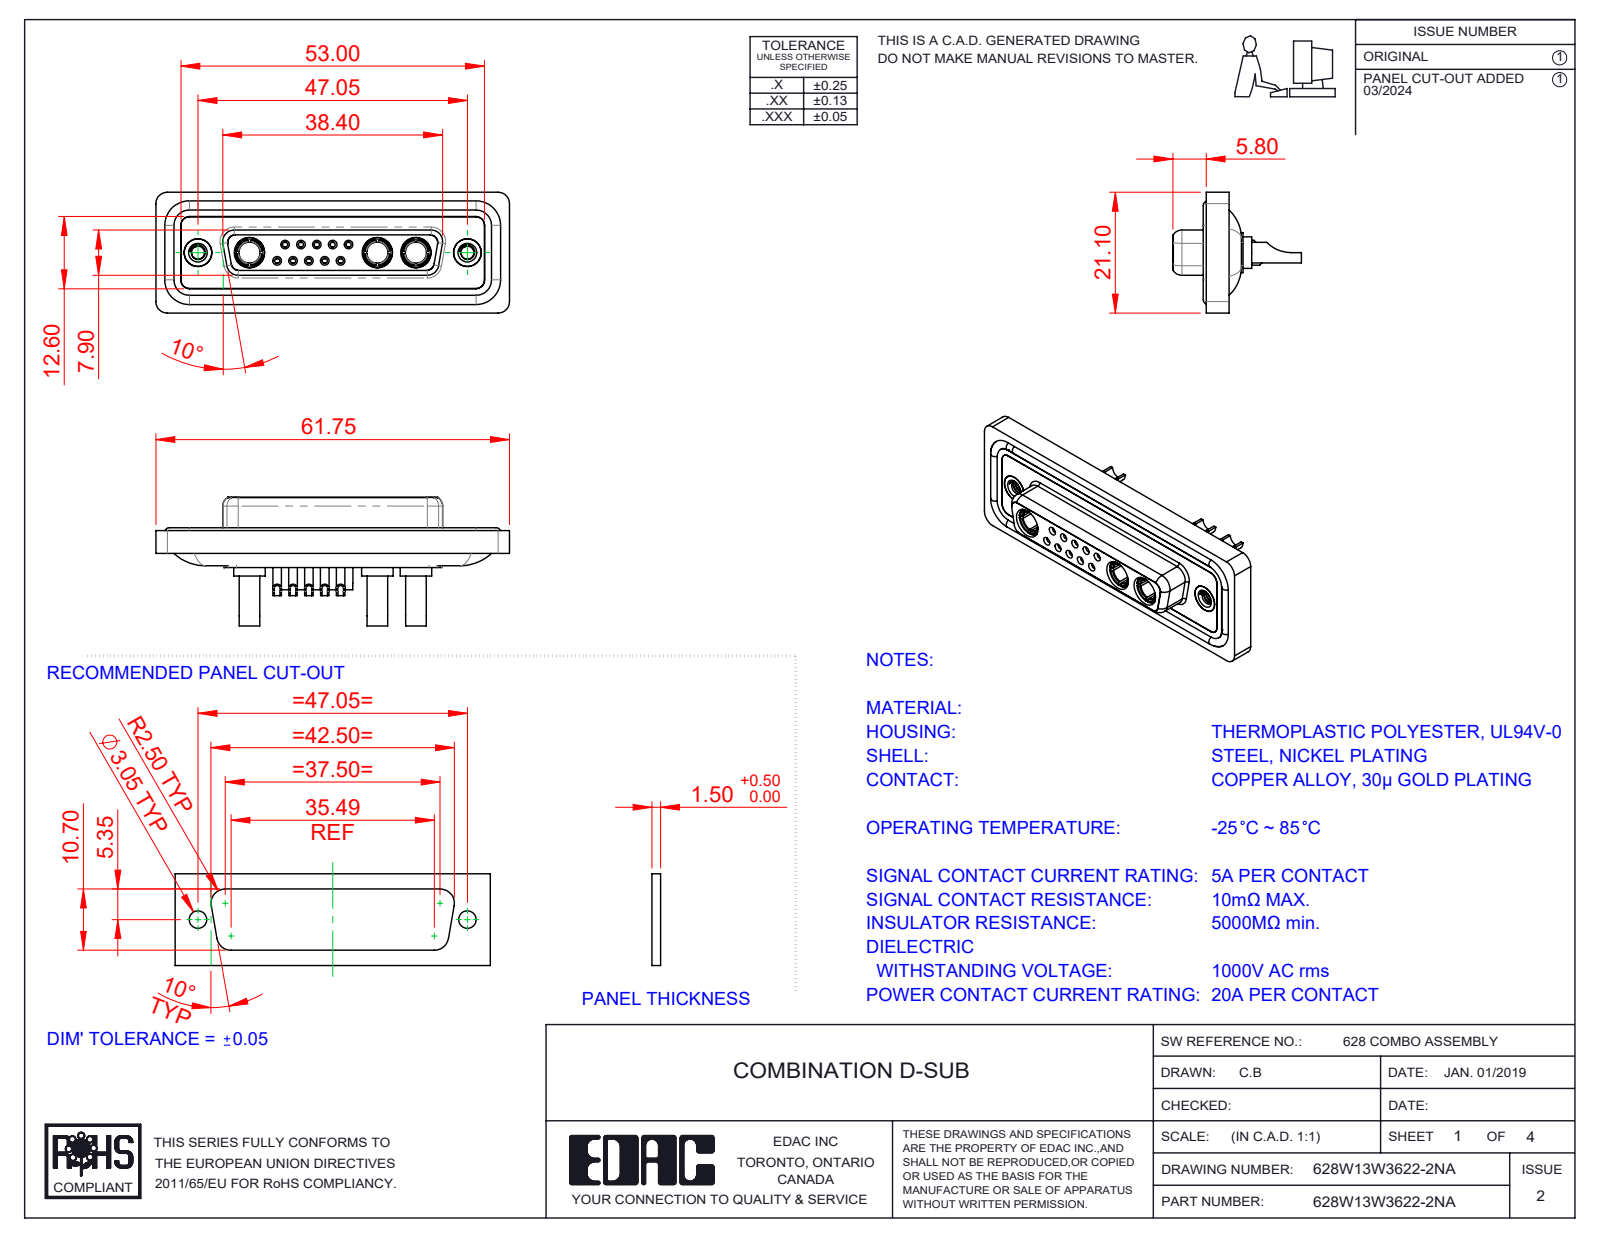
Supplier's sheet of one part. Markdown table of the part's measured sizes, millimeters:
| quantity | value |
| --- | --- |
| part name | 628Combo Housing_13W3; 628Combo Waterproof Housing_25 Contacts; 628W13W3622-2NA; Power Socket_20A SC (+5 more) |
| STEP written by | SolidWorks 2023 (CONFIG_CONTROL_DESIGN) |
| units | millimeters |
| bodies | 23 solids, 1174 faces (371 planar, 478 cylindrical, 325 other) |
| overall size | 61.75 × 22.45 × 21.1 |
| volume | 8 334 mm³ |
| surface area | 14 059 mm² |
| round holes (diameter × count) | 0.9 × 10, 1 × 10, 1.1 × 10, 1.5 × 10, 2 × 10, 1.6 × 5, 1.7 × 5, 4.85 × 5, 2.7 × 3, 3.7 × 3, 5.3 × 3, 2.26 × 2 |
| round bosses / shafts (diameter × count) | 2.2 × 10, 1.6 × 9, 5.5 × 3, 5.2 × 3, 4.96 × 3, 4.75 × 3, 3.75 × 3, 3.6 × 3 |
| partial cylindrical surfaces (radius × count) | 1.5 × 22, 2 × 18, 1.35 × 8, 1.6 × 8, 1 × 6, 0.25 × 4, 0.5 × 4, 0.6 × 4 |
| main face-to-face distances | 0.4, 1.8, 7.45, 5.65, 0.5, 6.6, 7.05, 1.6, 2.9, 1.1 |
| hole center spacings | 3.16, 2.77, 5.03, 5.04, 5.54, 8.31, 7.49, 2.76 |
